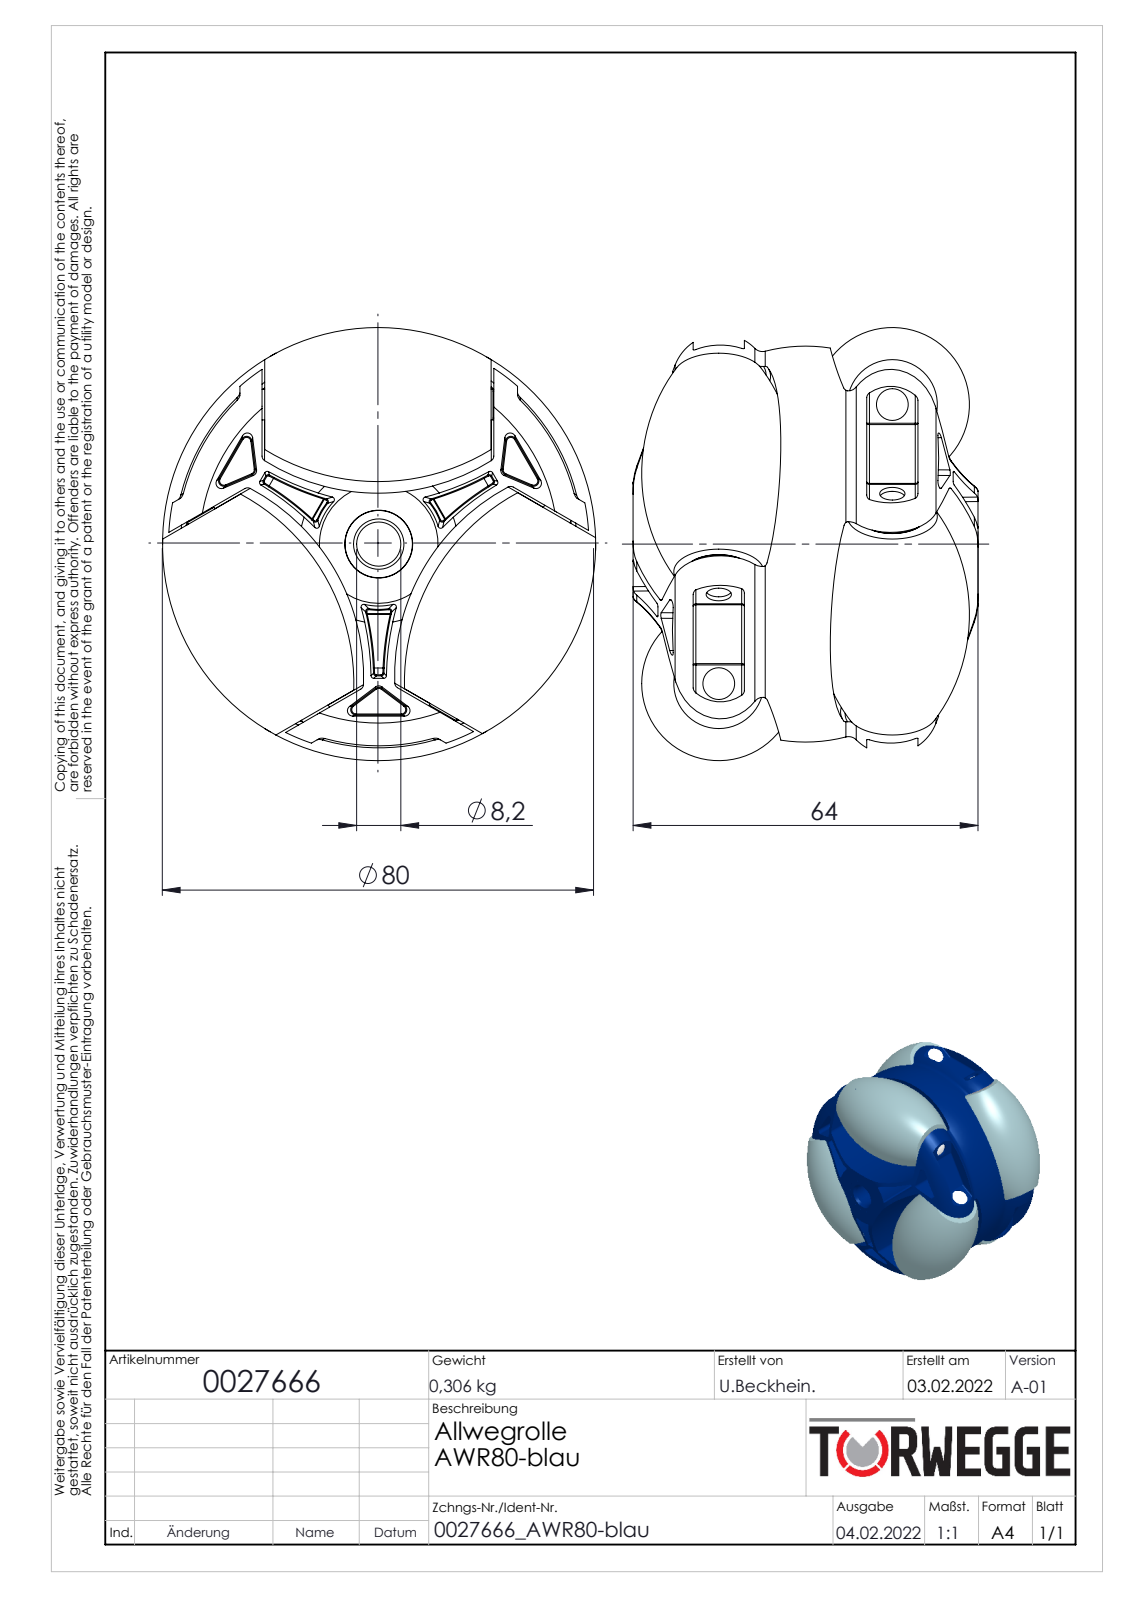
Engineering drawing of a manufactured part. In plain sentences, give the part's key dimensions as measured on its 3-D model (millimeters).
The part is named "0027666". Its 3-D file was written by "SolidWorks 2020 (AUTOMOTIVE_DESIGN)". It is 27 solids with 1011 faces: 158 planar, 367 cylindrical and 486 other. Overall it measures 80.4 by 80.35 by 64 millimeters. Its volume is 191 407 cubic millimeters and its surface area 86 477 square millimeters. Round holes: 7 of diameter 10.8, 7 of diameter 12.35, 7 of diameter 12.6, 6 of diameter 4.7, 6 of diameter 5.85, 6 of diameter 5.9, 1 of diameter 8.2. Round bosses or shafts: 7 of diameter 12.5, 6 of diameter 6, 6 of diameter 5.7, 6 of diameter 5. Partial cylindrical surfaces (rounded edges, fillets, slot ends): 48 of radius 0.5, 30 of radius 0.2, 30 of radius 1, 6 of radius 12.5, 6 of radius 39.65. The main face-to-face distances are 0.5, 42.5, 43, 42, 63.42, 30.5, 12, 12.5, 30, 12.2. The hole center spacings are 60.99.
